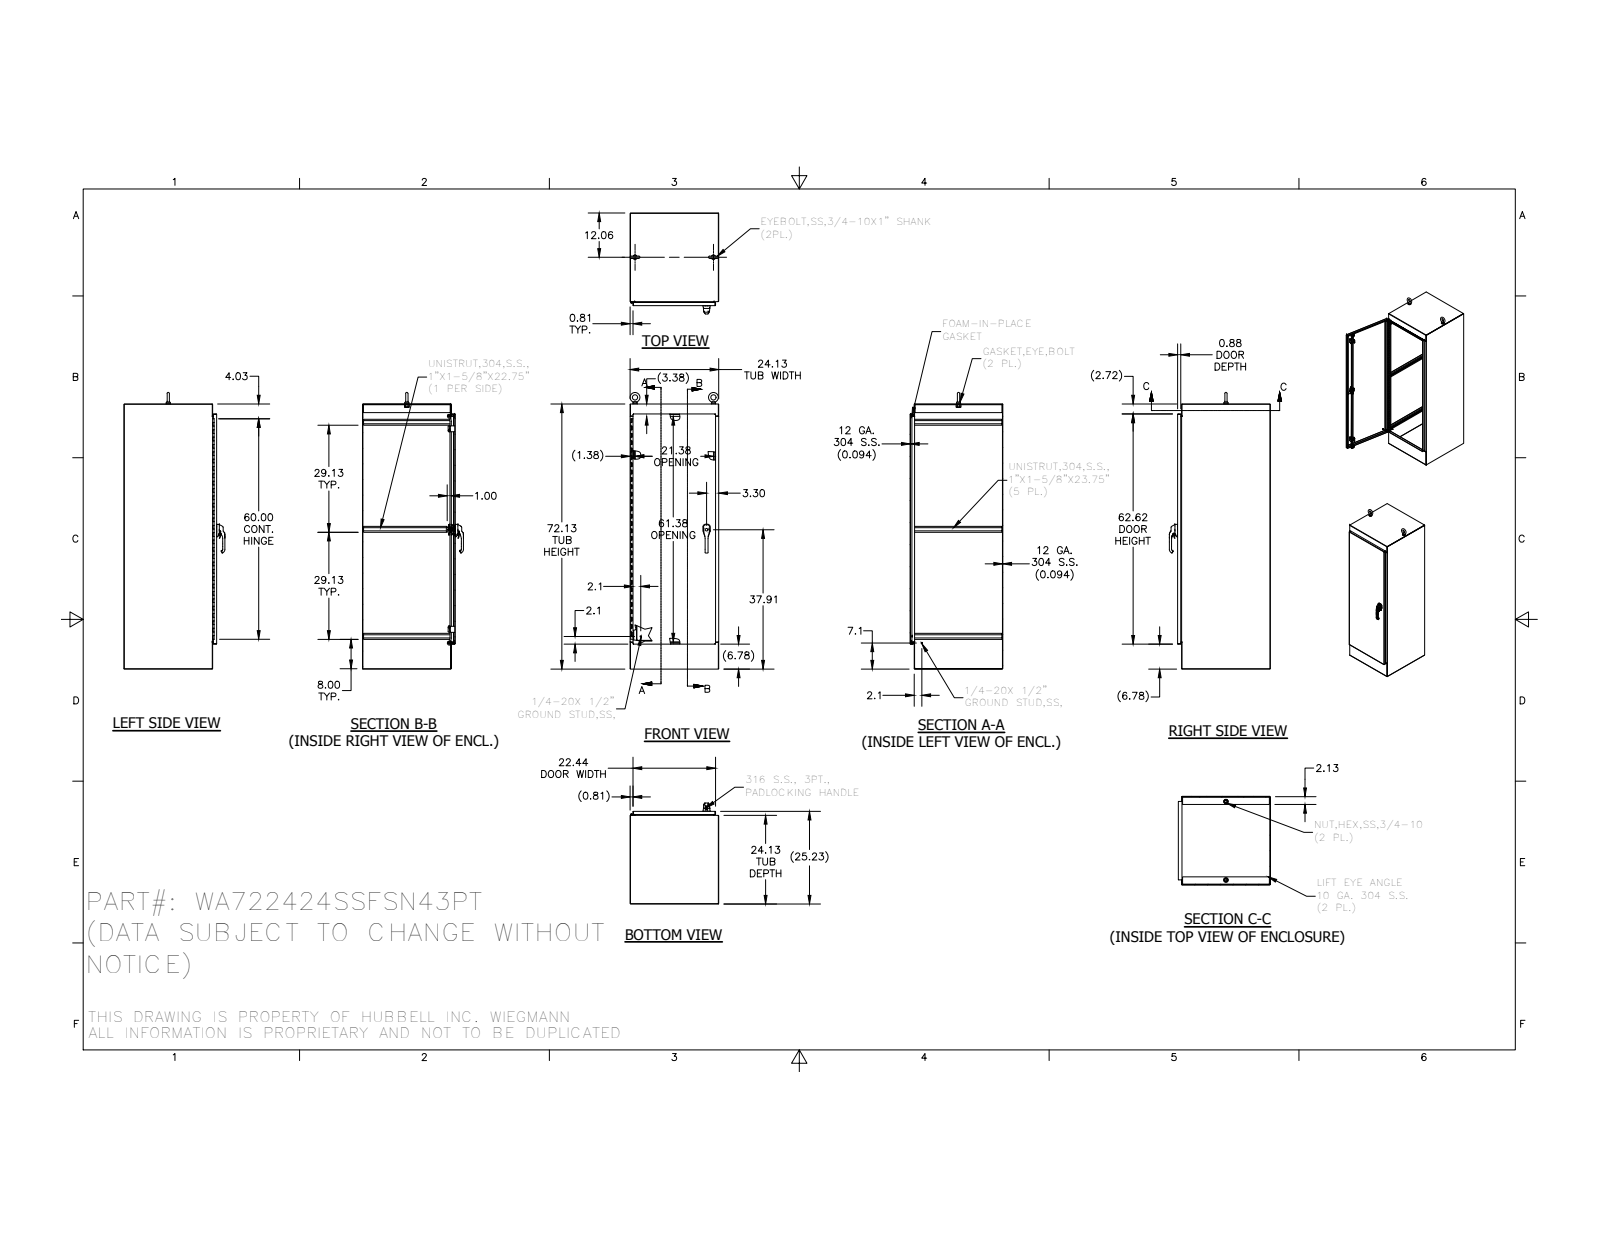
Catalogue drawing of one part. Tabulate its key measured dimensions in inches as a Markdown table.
| quantity | value |
| --- | --- |
| part name | 38846; SUPPORT-ROLL_AF0; 1091-74-03; 2100-11 (+8 more) |
| STEP written by | SolidWorks 2014 (AUTOMOTIVE_DESIGN) |
| units | inches |
| bodies | 66 solids, 3475 faces (1228 planar, 1307 cylindrical, 940 other) |
| overall size | 75.248 × 27.476 × 24.125 |
| volume | 950.2 in³ |
| surface area | 19 647 in² |
| round holes (diameter × count) | 0.262 × 8, 0.375 × 8, 0.187 × 4, 0.213 × 3, 0.25 × 3, 0.28 × 3, 0.241 × 2, 0.252 × 2, 0.315 × 2, 0.4 × 2, 0.402 × 2, 0.413 × 2 |
| round bosses / shafts (diameter × count) | 1 × 3, 0.236 × 3, 1.25 × 2, 1.12 × 2, 0.75 × 2, 0.563 × 2, 0.533 × 2, 0.531 × 2 |
| partial cylindrical surfaces (radius × count) | 0.02 × 172, 0.012 × 107, 0.125 × 26, 0.019 × 21, 0.05 × 19, 0.031 × 17, 0.079 × 14, 0.059 × 13 |
| main face-to-face distances | 0.094, 24.031, 25.133, 23.937, 24.125, 25.039, 25.227, 72.031, 1.102, 71.937 |
| hole center spacings | 6.667, 20, 0.38, 0.76, 2.763, 13.333, 26.667, 0.38 |
